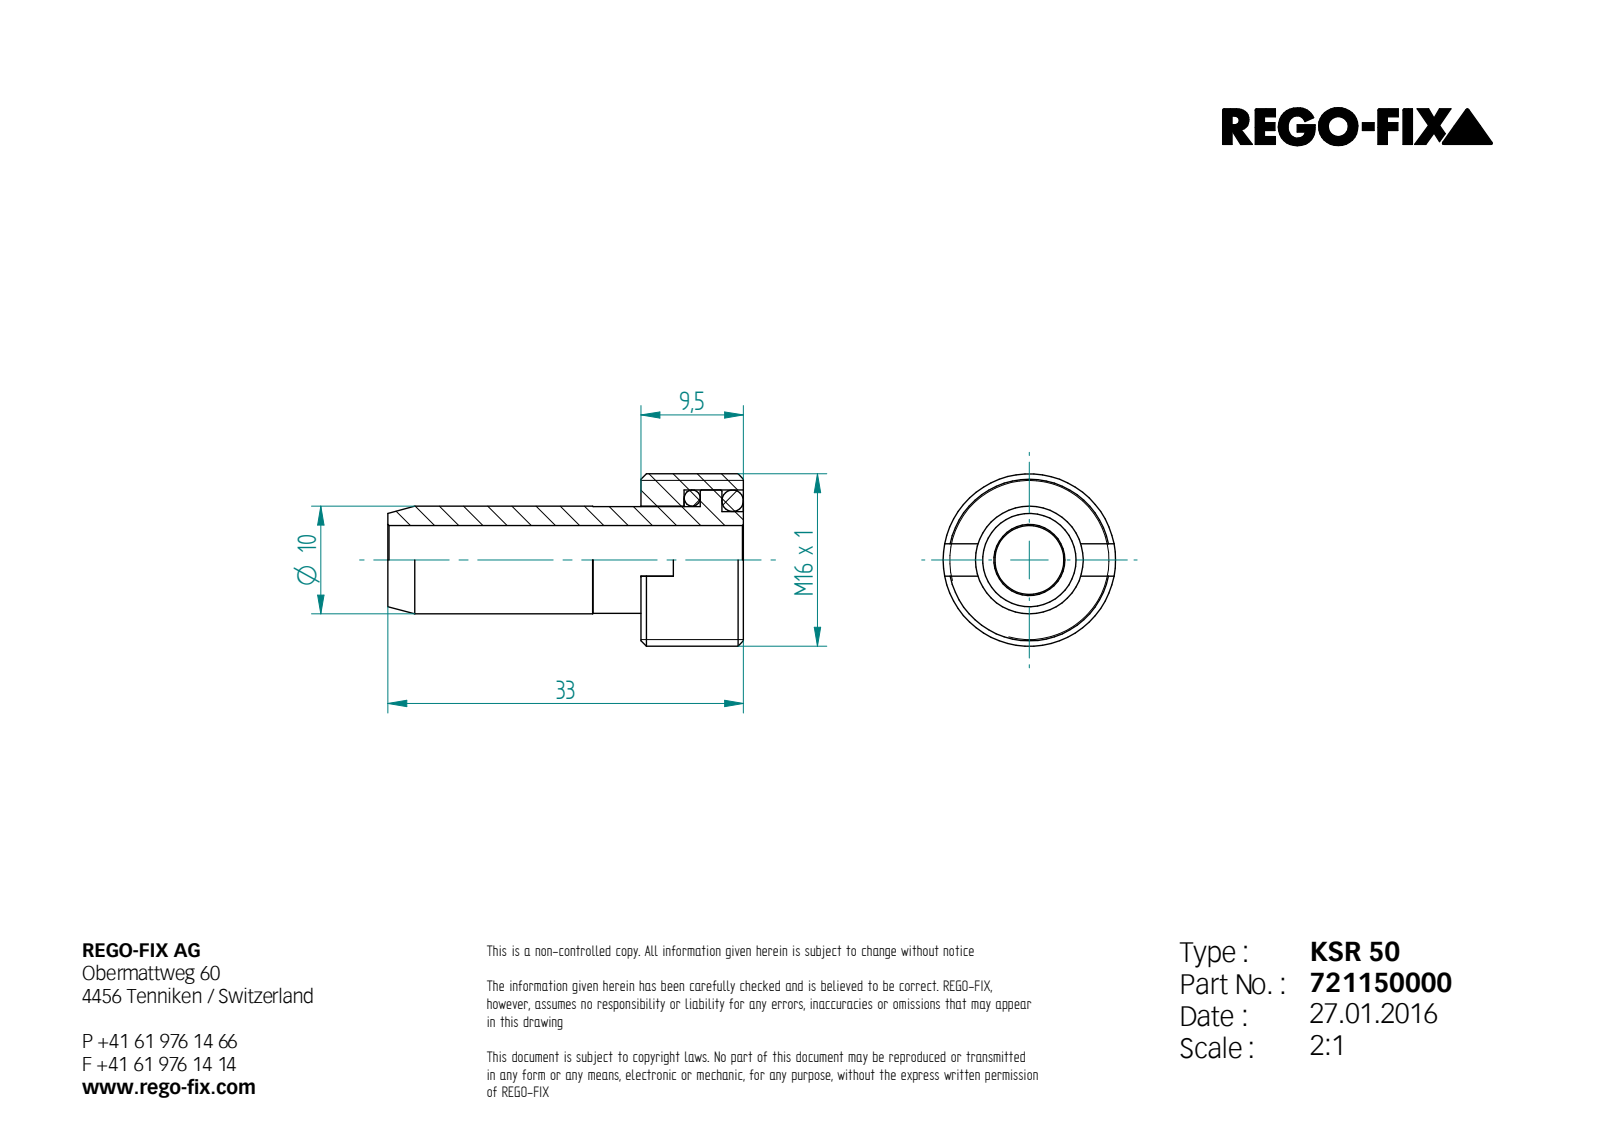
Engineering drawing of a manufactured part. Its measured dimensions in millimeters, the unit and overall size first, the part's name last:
Units: millimetres
Overall size (bounding box): 33 × 16 × 16
Round holes (diameter × count): ⌀6.4 ×1, ⌀10 ×1, ⌀13 ×1
Round bosses / shafts (diameter × count): ⌀16 ×1, ⌀9.9 ×1, ⌀9 ×1
Main face-to-face distances: 2, 4, 5.5, 9.5, 7.5, 3.5, 1.5, 3, 23.5, 27.5
Volume: 2 540 mm³ · Surface area: 3 316 mm²
Bodies: 4 solids, 33 faces (14 planar, 8 cylindrical, 11 other)
Part name (STEP PRODUCT): 0004177; 0012553; 0012554; 0004175
STEP written by: Unknown (AUTOMOTIVE_DESIGN)
